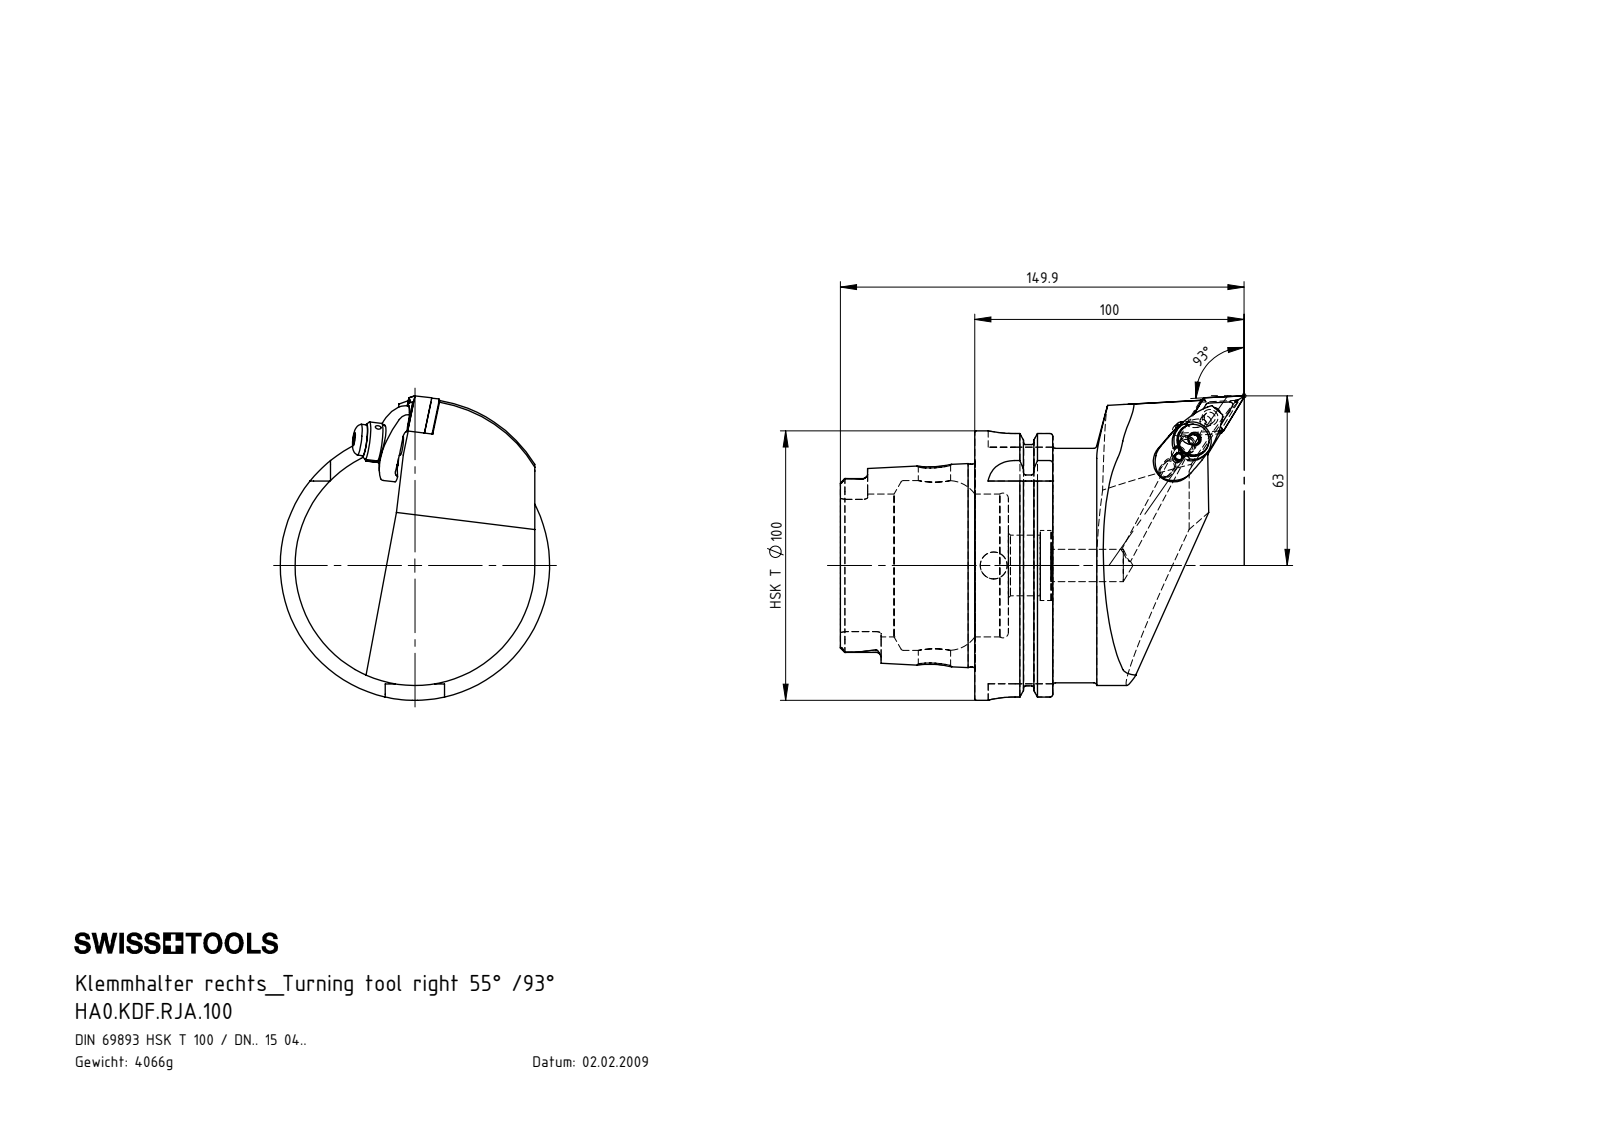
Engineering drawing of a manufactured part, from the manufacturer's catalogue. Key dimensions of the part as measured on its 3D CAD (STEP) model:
Part name (STEP PRODUCT): WDF-ER2.101.003_A; HA0.KDF.RJA.100; WCC-ER5.102.005_A; WCC-ER3.102.024_C (+7 more)
STEP written by: SolidWorks 2017 (AUTOMOTIVE_DESIGN)
Units: millimetres
Bodies: 11 solids, 467 faces (121 planar, 154 cylindrical, 192 other)
Overall size (bounding box): 149.9 × 113 × 100
Volume: 518 876 mm³ · Surface area: 72 694 mm²
Round holes (diameter × count): ⌀2 ×3, ⌀5 ×3, ⌀7 ×2, ⌀12 ×2, ⌀2.4 ×1, ⌀3 ×1, ⌀4.2 ×1, ⌀5.16 ×1, ⌀6 ×1, ⌀6.2 ×1, ⌀6.5 ×1, ⌀8.5 ×1
Round bosses / shafts (diameter × count): ⌀6 ×2, ⌀3 ×2, ⌀100 ×1, ⌀91.95 ×1, ⌀87 ×1, ⌀75.26 ×1, ⌀14 ×1, ⌀11.5 ×1
Partial cylindrical surfaces — rounded edges, fillets, slot ends (radius × count): R0.39 ×6, R0.69 ×6, R1.9 ×6, R0.4 ×4, R10 ×4, R1.5 ×3, R0.8 ×2, R2 ×2
Main face-to-face distances: 12.45, 16.5, 28.95, 49.9, 62.35, 78.85, 87.8, 78.2, 28.3, 15.85
Hole centre spacings: 7.9, 7.91, 8.2, 15, 15.1, 14.7, 14.8, 22.9
